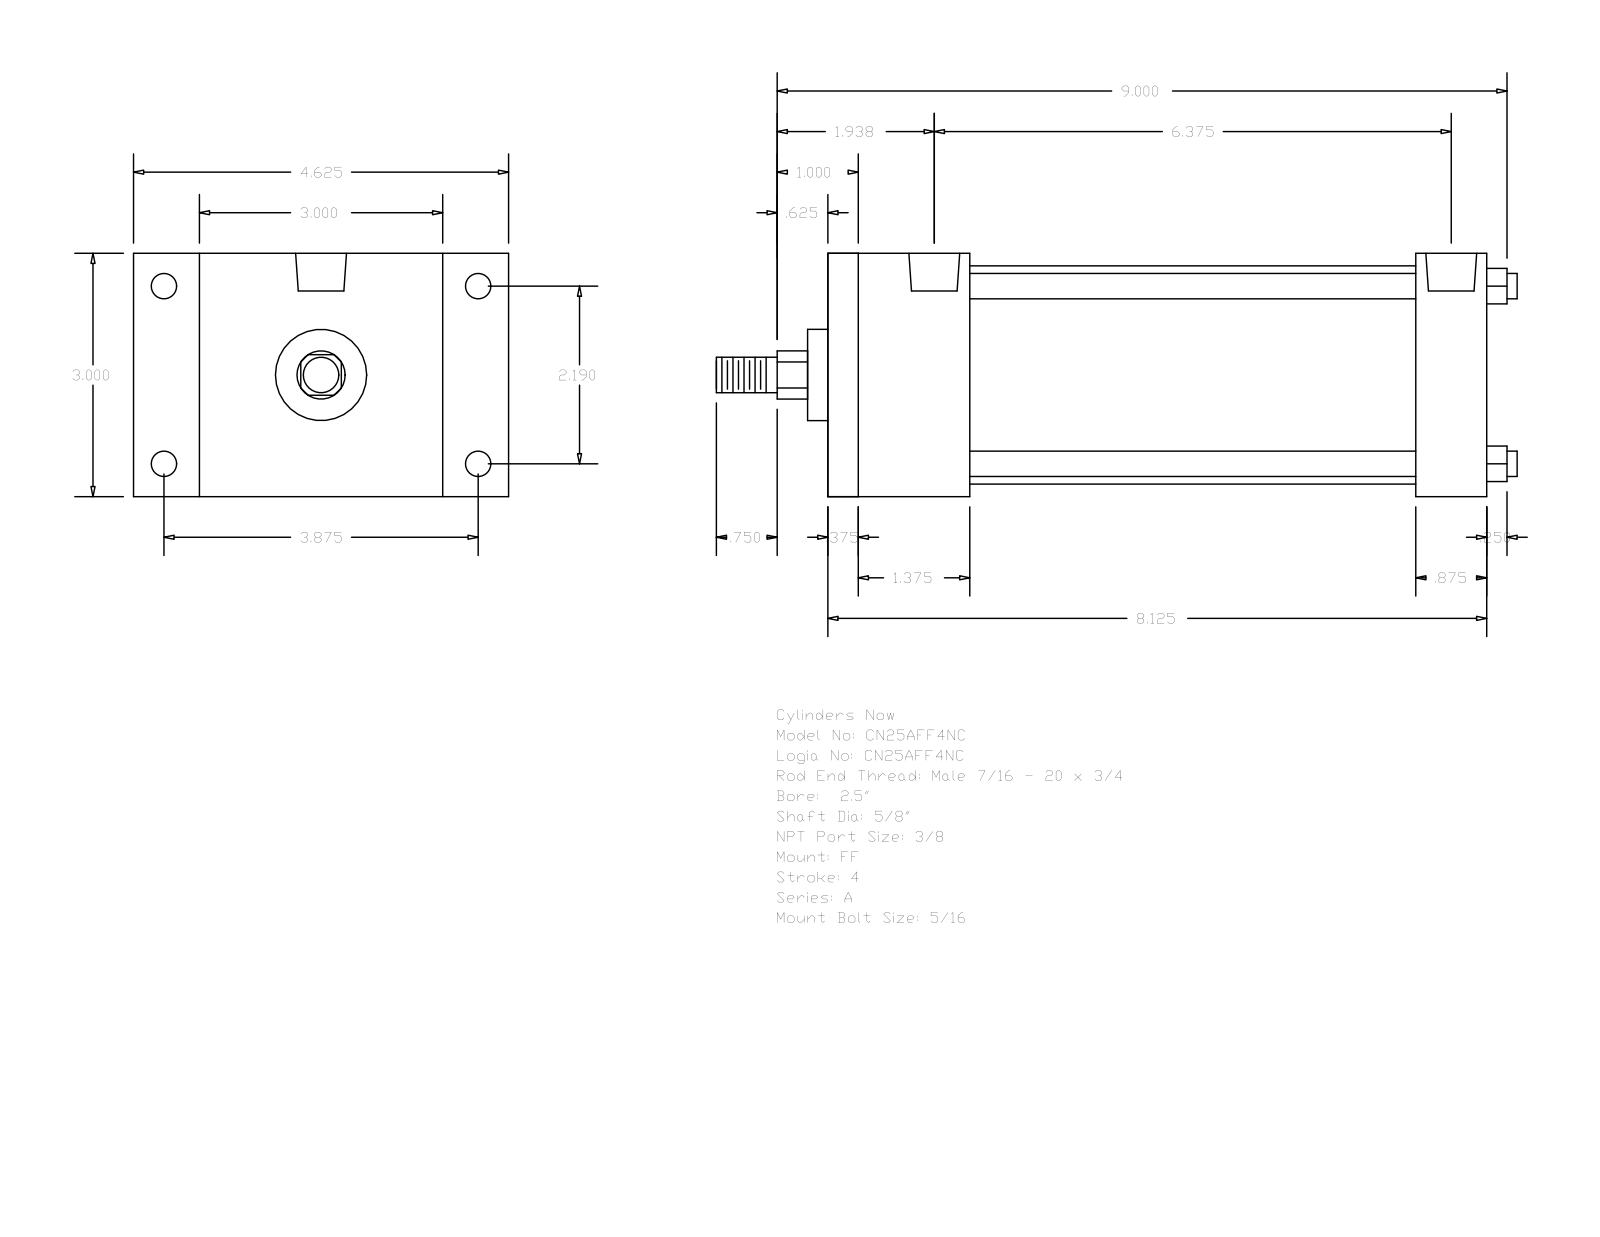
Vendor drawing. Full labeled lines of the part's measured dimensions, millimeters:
Part name (STEP PRODUCT): A_FF__0250_0.625
STEP written by: GSSL Pune (CONFIG_CONTROL_DESIGN)
Units: millimetres
Bodies: 0 solids, 92 faces (64 planar, 28 cylindrical, 0 other)
Overall size (bounding box): 250.82 × 117.47 × 76.2
Round holes (diameter × count): ⌀5.56 ×4, ⌀7.94 ×4, ⌀15.93 ×2
Round bosses / shafts (diameter × count): ⌀7.94 ×4, ⌀68.33 ×1, ⌀28.57 ×1, ⌀15.88 ×1, ⌀11.11 ×1
Partial cylindrical surfaces — rounded edges, fillets, slot ends (radius × count): R7.54 ×1
Main face-to-face distances: 76.2, 206.37, 9.52, 196.85, 44.45, 34.93, 184.15, 174.63, 139.7, 161.92
Hole centre spacings: 2.38, 55.62, 98.42, 113.05, 164.31, 166.69, 161.93
